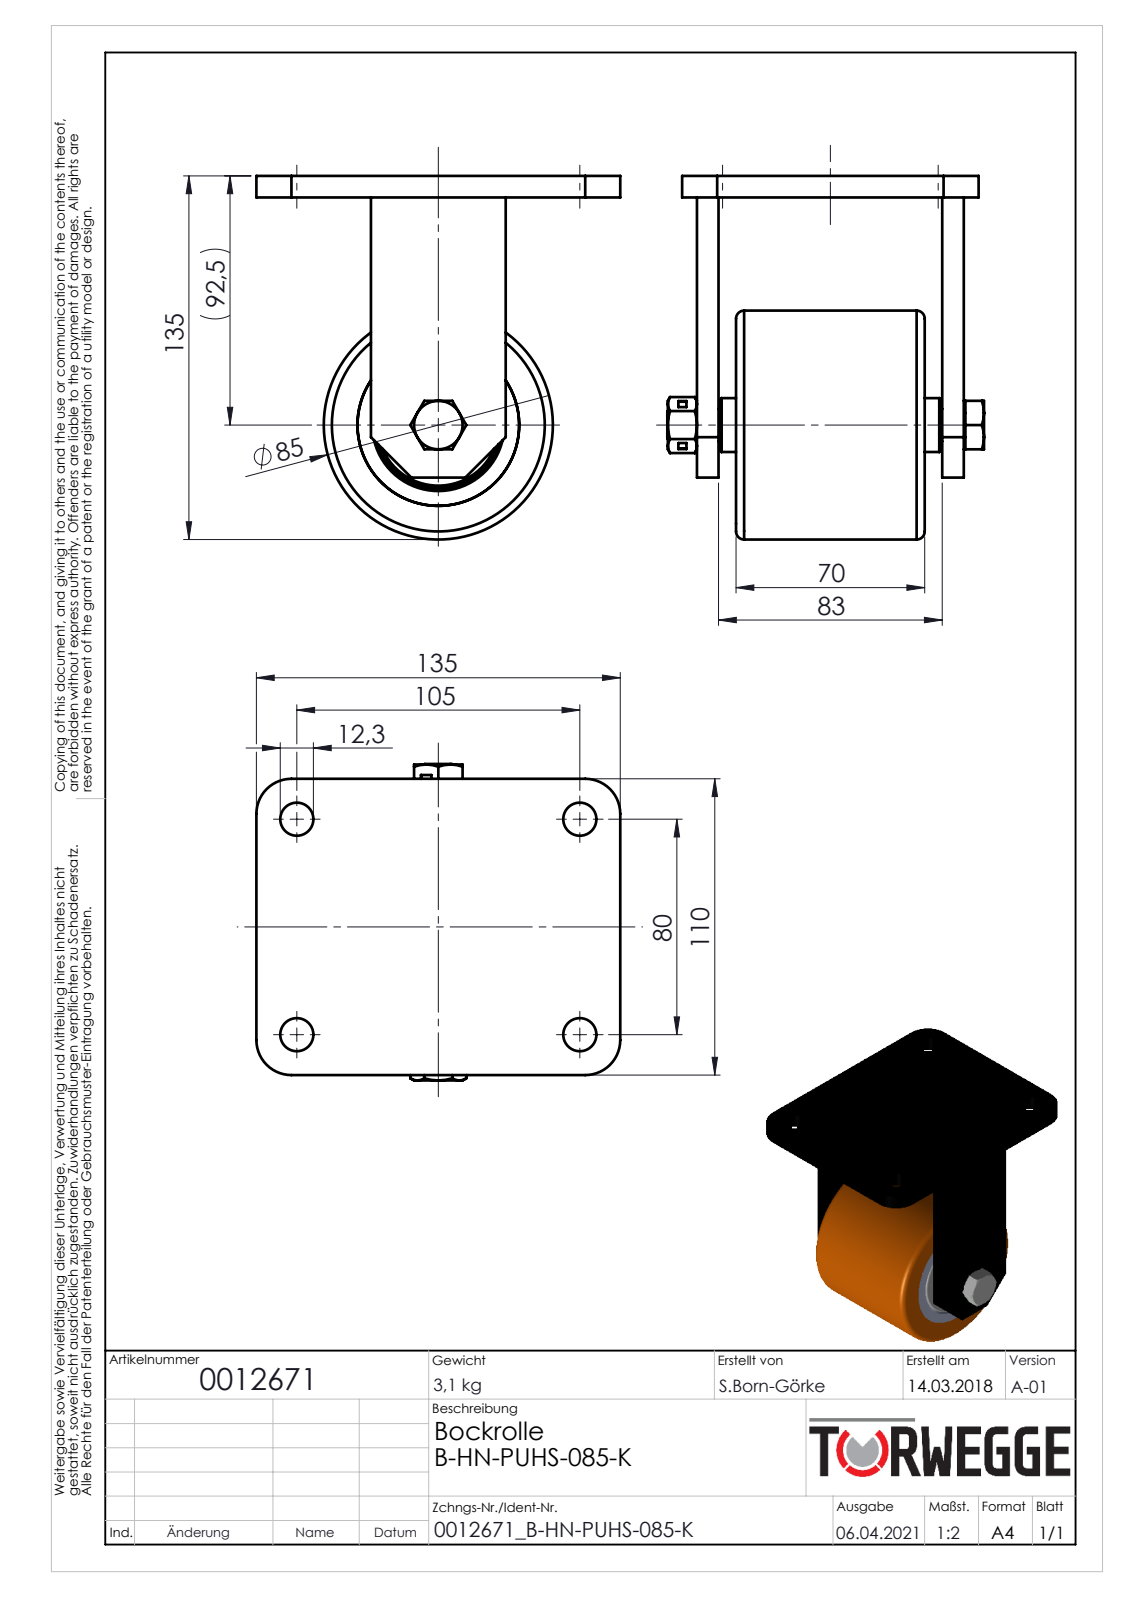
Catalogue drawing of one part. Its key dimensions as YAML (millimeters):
part_name: "0012671"
step_written_by: "SolidWorks 2020 (AUTOMOTIVE_DESIGN)"
units: millimeters
bodies: {solids: 18, faces: 242, planar: 84, cylindrical: 80, other: 78}
overall_size: [135, 135, 117.5]
volume: 545936
surface_area: 161164
round_holes:
  - {diameter: 12.3, count: 4}
  - {diameter: 10.2, count: 1}
  - {diameter: 12, count: 1}
  - {diameter: 12.4, count: 1}
  - {diameter: 12.5, count: 1}
  - {diameter: 20, count: 1}
  - {diameter: 28.1, count: 1}
  - {diameter: 38.9, count: 1}
  - {diameter: 42, count: 1}
  - {diameter: 47, count: 1}
  - {diameter: 60, count: 1}
round_bosses_or_shafts:
  - {diameter: 85, count: 1}
  - {diameter: 18, count: 1}
partial_cylinders:
  - {radius: 13, count: 4}
face_to_face_distances: [8, 91, 76.5, 14.5, 84.5, 6.5, 99, 83, 56, 70]
hole_center_spacings: [80, 105, 132]
